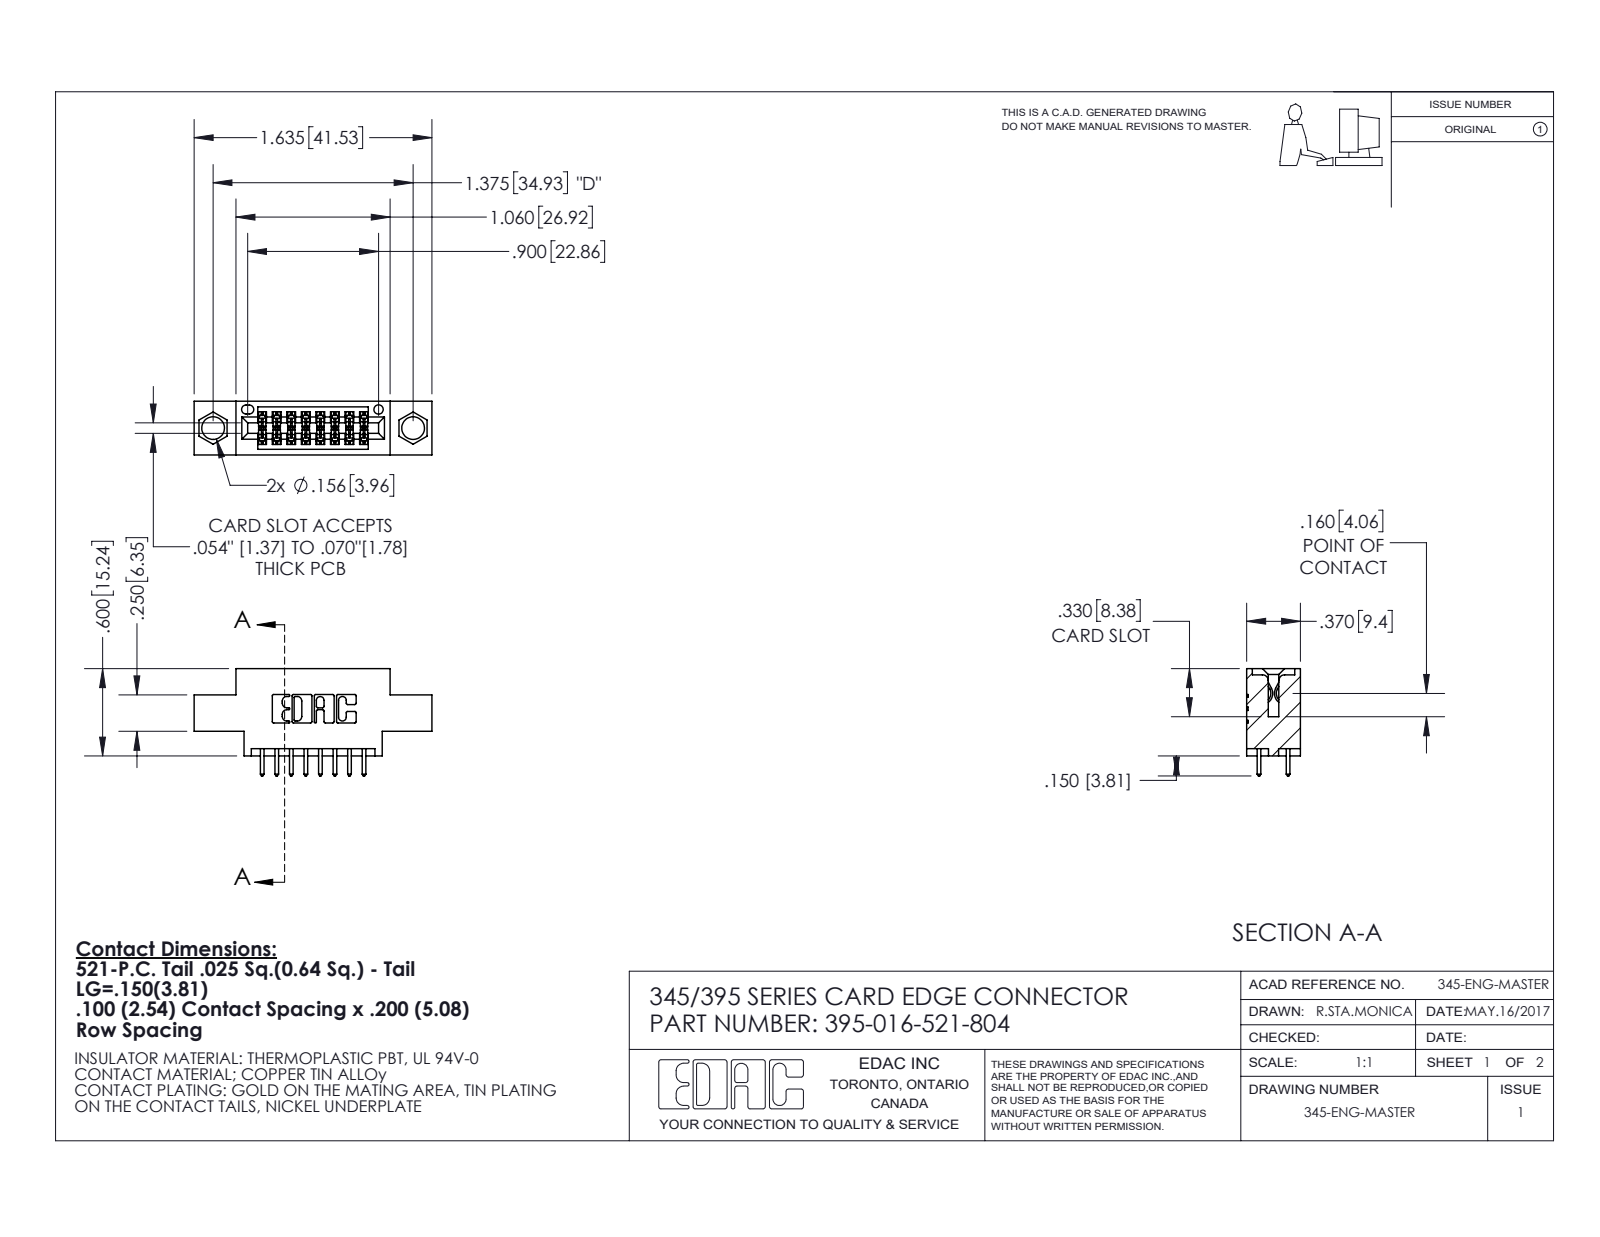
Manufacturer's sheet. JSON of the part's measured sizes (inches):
{"part_name": "395-016-521-804; 345 Part_0.170 Offset - 0.156 Dia-TI; 345-292-001_345-293-121", "step_written_by": "SolidWorks 2020 (CONFIG_CONTROL_DESIGN)", "units": "inches", "bodies": {"solids": 17, "faces": 944, "planar": 626, "cylindrical": 318, "other": 0}, "overall_size": [1.635, 0.737, 0.37], "volume_in3": 0.213, "surface_area_in2": 6.908, "round_holes": [[0.156, 2], [0.064, 1]], "partial_cylinders_radius": [[0.006, 32], [0.01, 22], [0.01, 16], [0.007, 6], [0.031, 6], [0.026, 3], [0.014, 2], [0.019, 2]], "face_to_face_distances": [0.2, 0.37, 0.072, 0.298, 0.1, 0.098, 0.272, 0.025, 0.225, 0.06], "hole_center_spacings": [0.27, 1.144, 1.375]}
